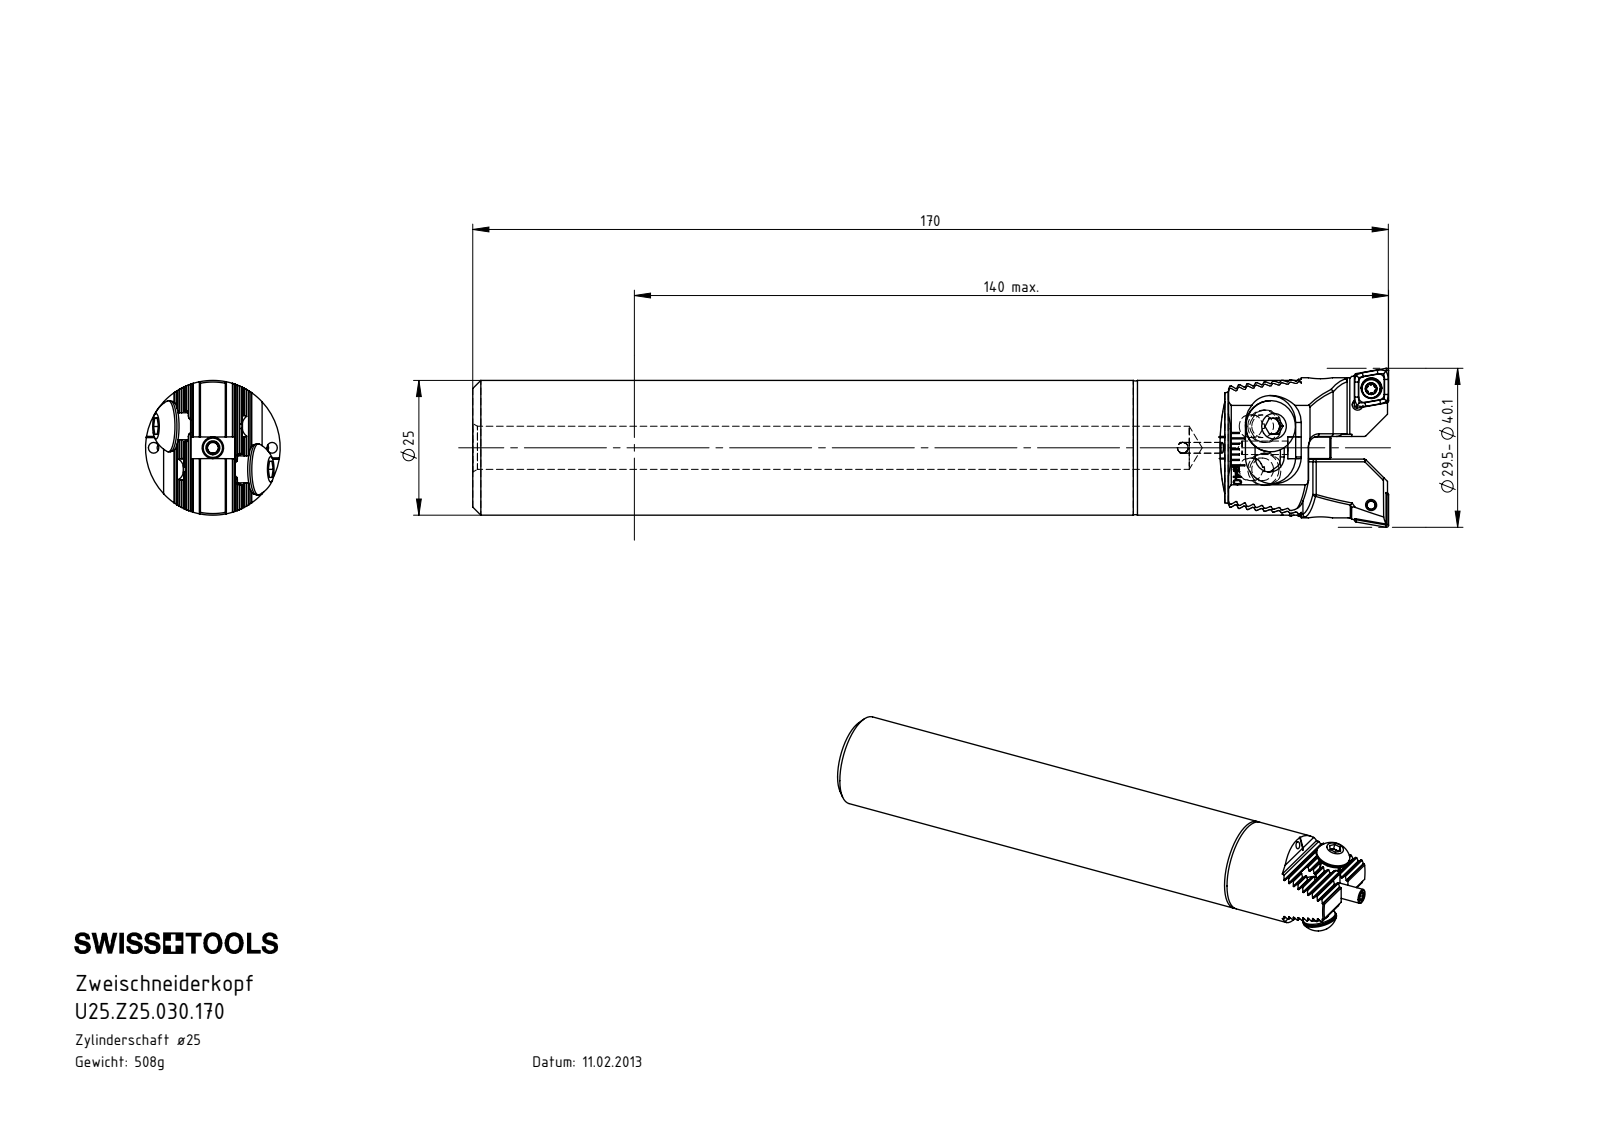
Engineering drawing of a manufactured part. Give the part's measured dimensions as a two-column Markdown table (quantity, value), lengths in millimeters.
| quantity | value |
| --- | --- |
| part name | Z25-ER1.003.012_A_gespannt; Z25-ER1.001.012; Z20-ER2.001.013_A; U25.Z25.K23.170 (+2 more) |
| STEP written by | SolidWorks 2017 (AUTOMOTIVE_DESIGN) |
| units | millimeters |
| bodies | 6 solids, 260 faces (166 planar, 62 cylindrical, 32 other) |
| overall size | 159.3 × 25 × 25 |
| volume | 65 334 mm³ |
| surface area | 17 975 mm² |
| round holes (diameter × count) | 2 × 4, 4.2 × 2, 5.3 × 2, 6 × 2, 2.5 × 1, 8 × 1 |
| round bosses / shafts (diameter × count) | 9.5 × 2, 9.2 × 2, 5 × 2, 25 × 1, 4 × 1, 3 × 1, 2.2 × 1 |
| partial cylindrical surfaces (radius × count) | 0.12 × 18, 220 × 2 |
| main face-to-face distances | 1.43, 2.86, 8.57, 4.29, 7.14, 5.71, 4.28, 2.85, 5.72, 10 |
